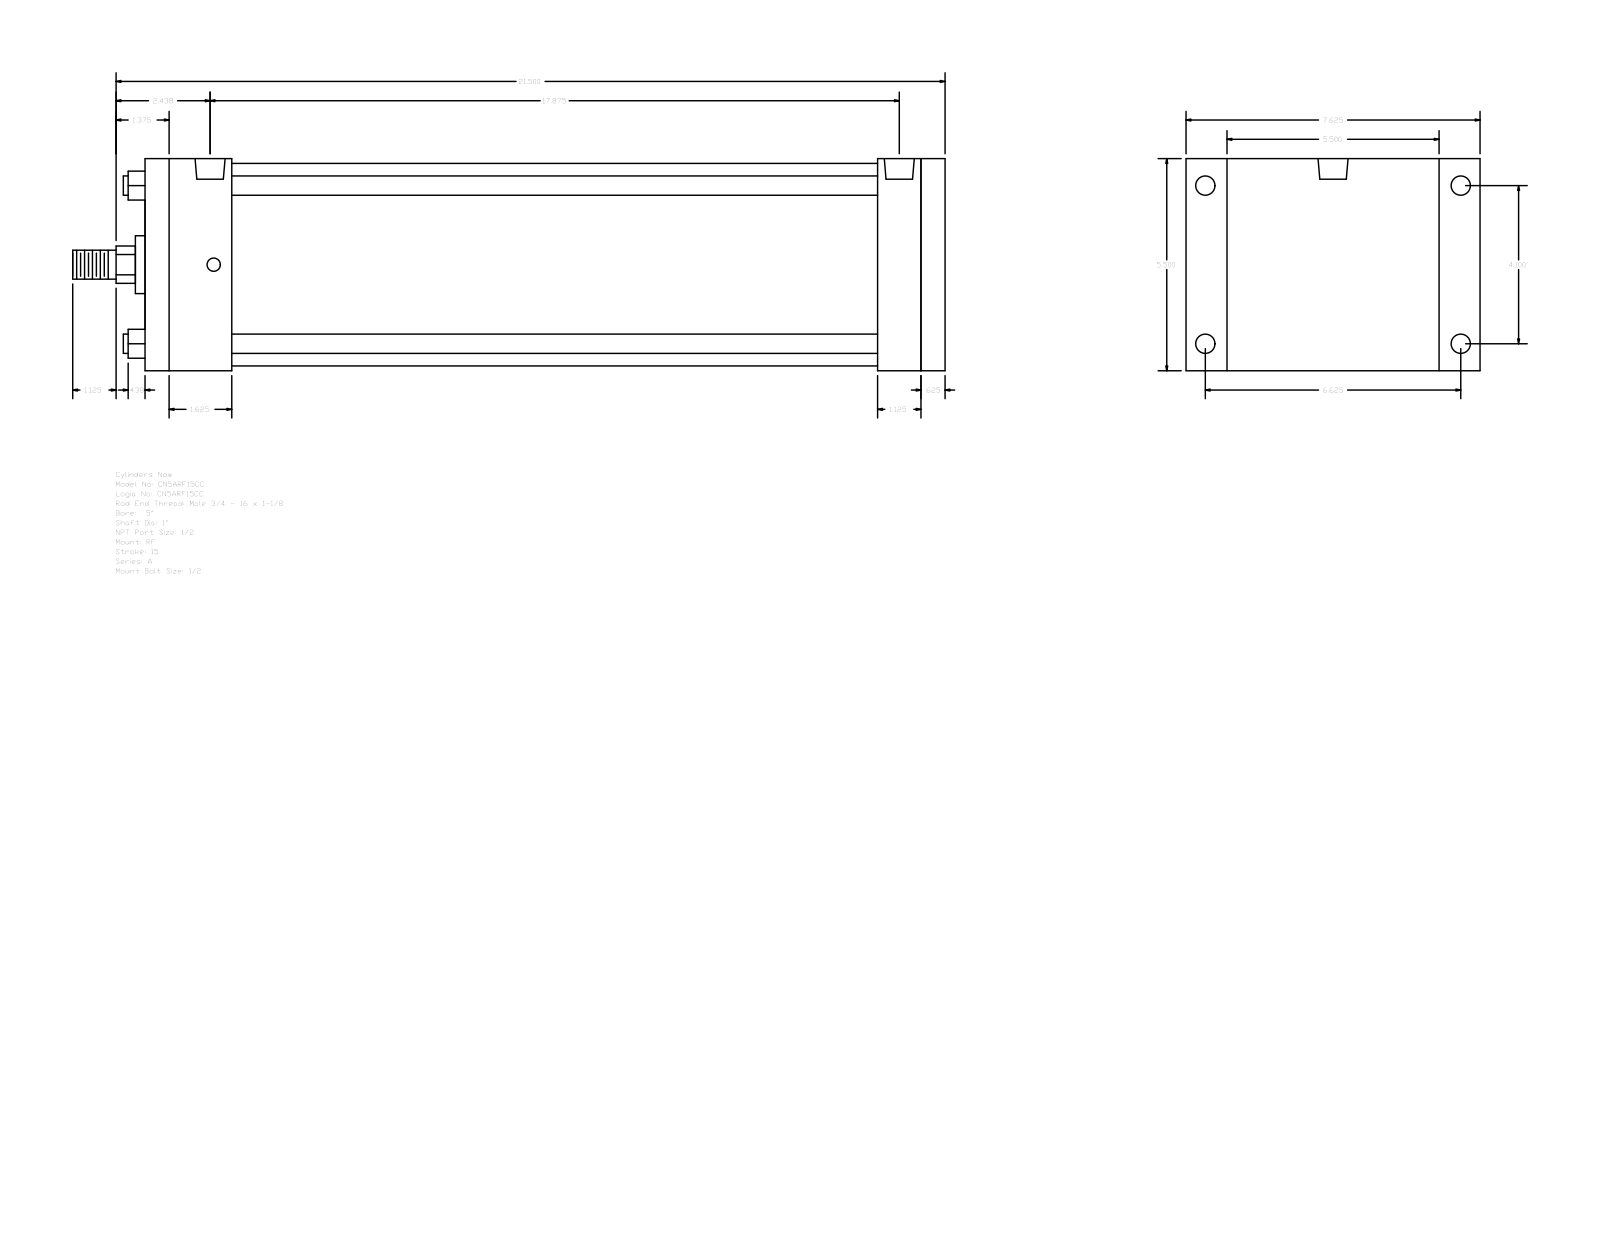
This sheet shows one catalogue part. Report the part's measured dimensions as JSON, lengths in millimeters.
{"part_name": "A_RF__0500_1", "step_written_by": "GSSL Pune (CONFIG_CONTROL_DESIGN)", "units": "millimeters", "bodies": {"solids": 0, "faces": 92, "planar": 64, "cylindrical": 28, "other": 0}, "overall_size": [574.67, 193.68, 139.7], "round_holes": [[8.73, 4], [12.7, 4], [19.77, 2]], "round_bosses_or_shafts": [[12.7, 4], [133.35, 1], [38.1, 1], [25.4, 1], [19.05, 1]], "partial_cylinders_radius": [[12.29, 1]], "face_to_face_distances": [139.7, 527.05, 511.18, 15.87, 57.15, 454.03, 469.9, 482.6, 425.45, 28.58], "hole_center_spacings": [2.39, 104.14, 168.28, 197.9, 449.25, 451.64, 454.03]}
